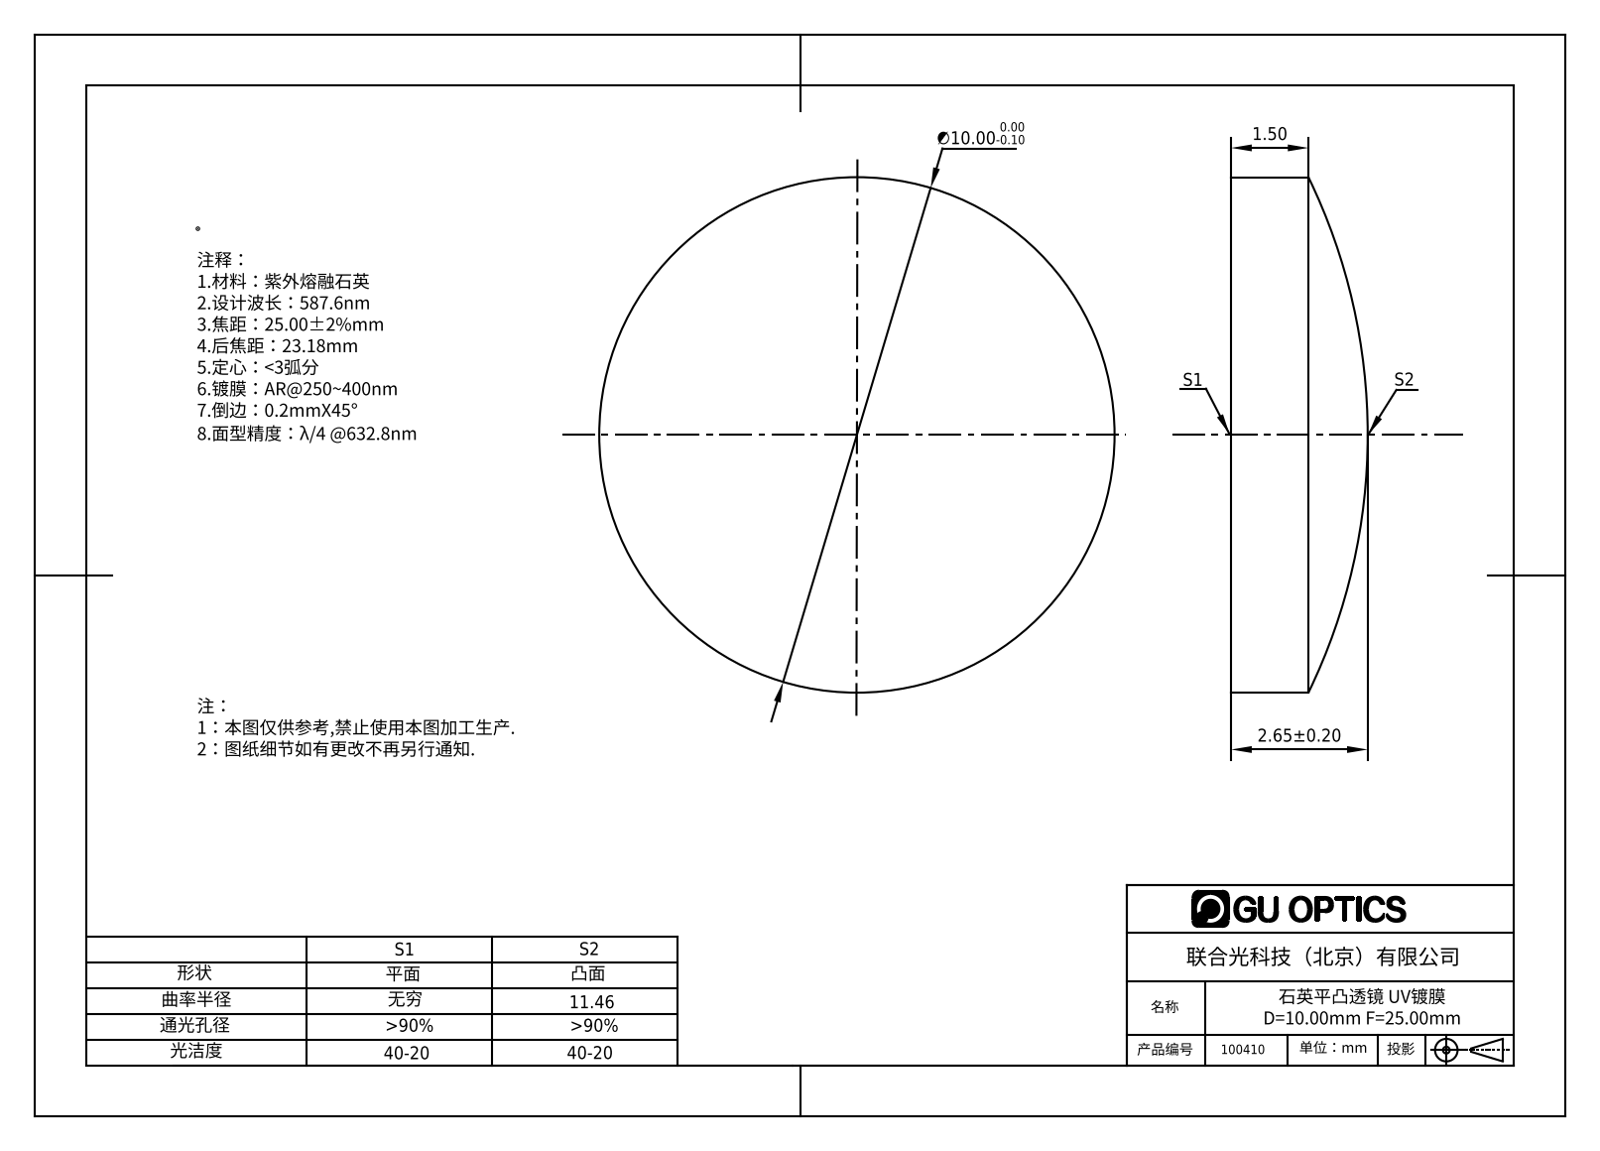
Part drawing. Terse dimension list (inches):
name: 100360
written by: SolidWorks 2016 (AUTOMOTIVE_DESIGN)
unit: in
bodies: 1 solid, 5 faces (1 planar, 2 cylindrical, 2 other)
size: 0.394 × 0.394 × 0.104
volume: 0.01 in³; area: 0.322 in²
bosses: 1× ⌀0.394
